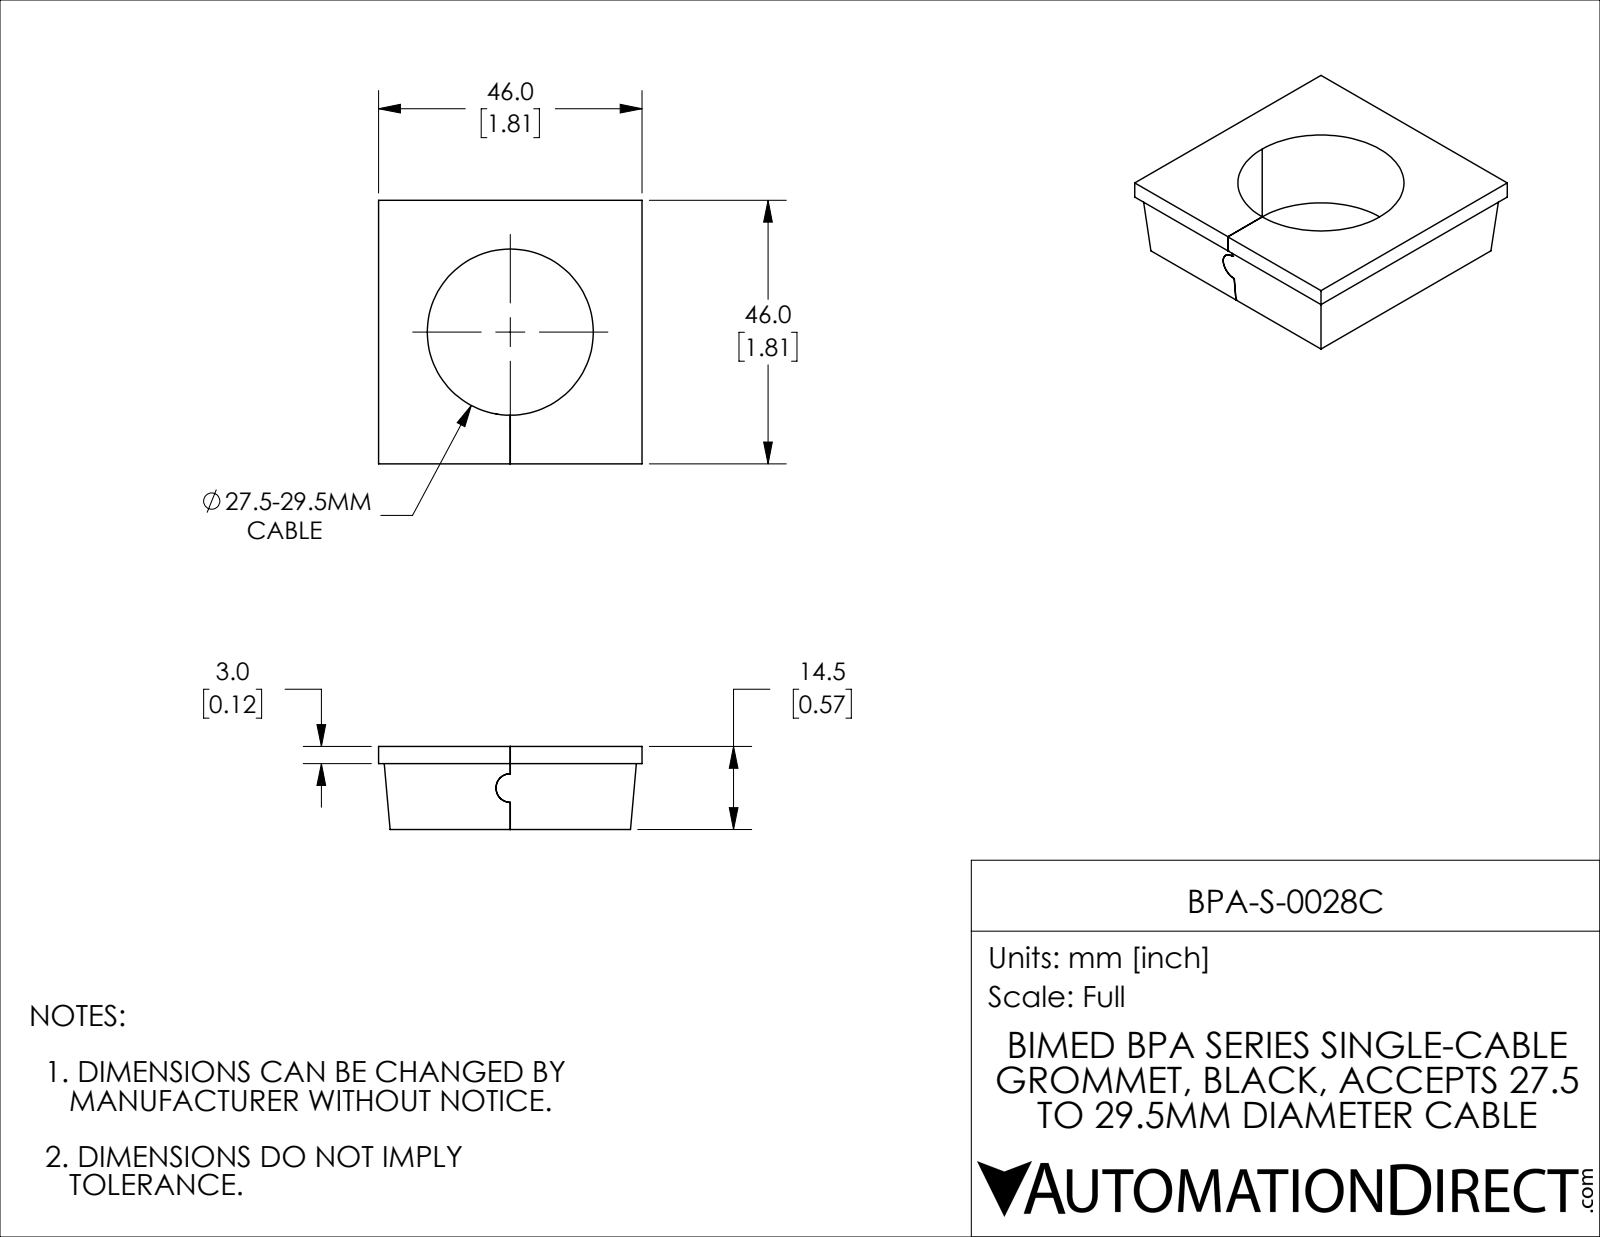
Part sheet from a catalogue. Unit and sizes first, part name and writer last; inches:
Units: inches
Overall size (bounding box): 1.811 × 1.811 × 0.571
Round holes (diameter × count): ⌀1.142 ×1
Partial cylindrical surfaces — rounded edges, fillets, slot ends (radius × count): R0.098 ×1, R0.099 ×1
Main face-to-face distances: 0.571, 1.811, 0.453, 0.118, 0.905, 0.906
Volume: 1.1 in³ · Surface area: 10.62 in²
Bodies: 1 solid, 22 faces (17 planar, 5 cylindrical, 0 other)
Part name (STEP PRODUCT): BPA-S-0028C
STEP written by: SolidWorks 2021 (CONFIG_CONTROL_DESIGN)
